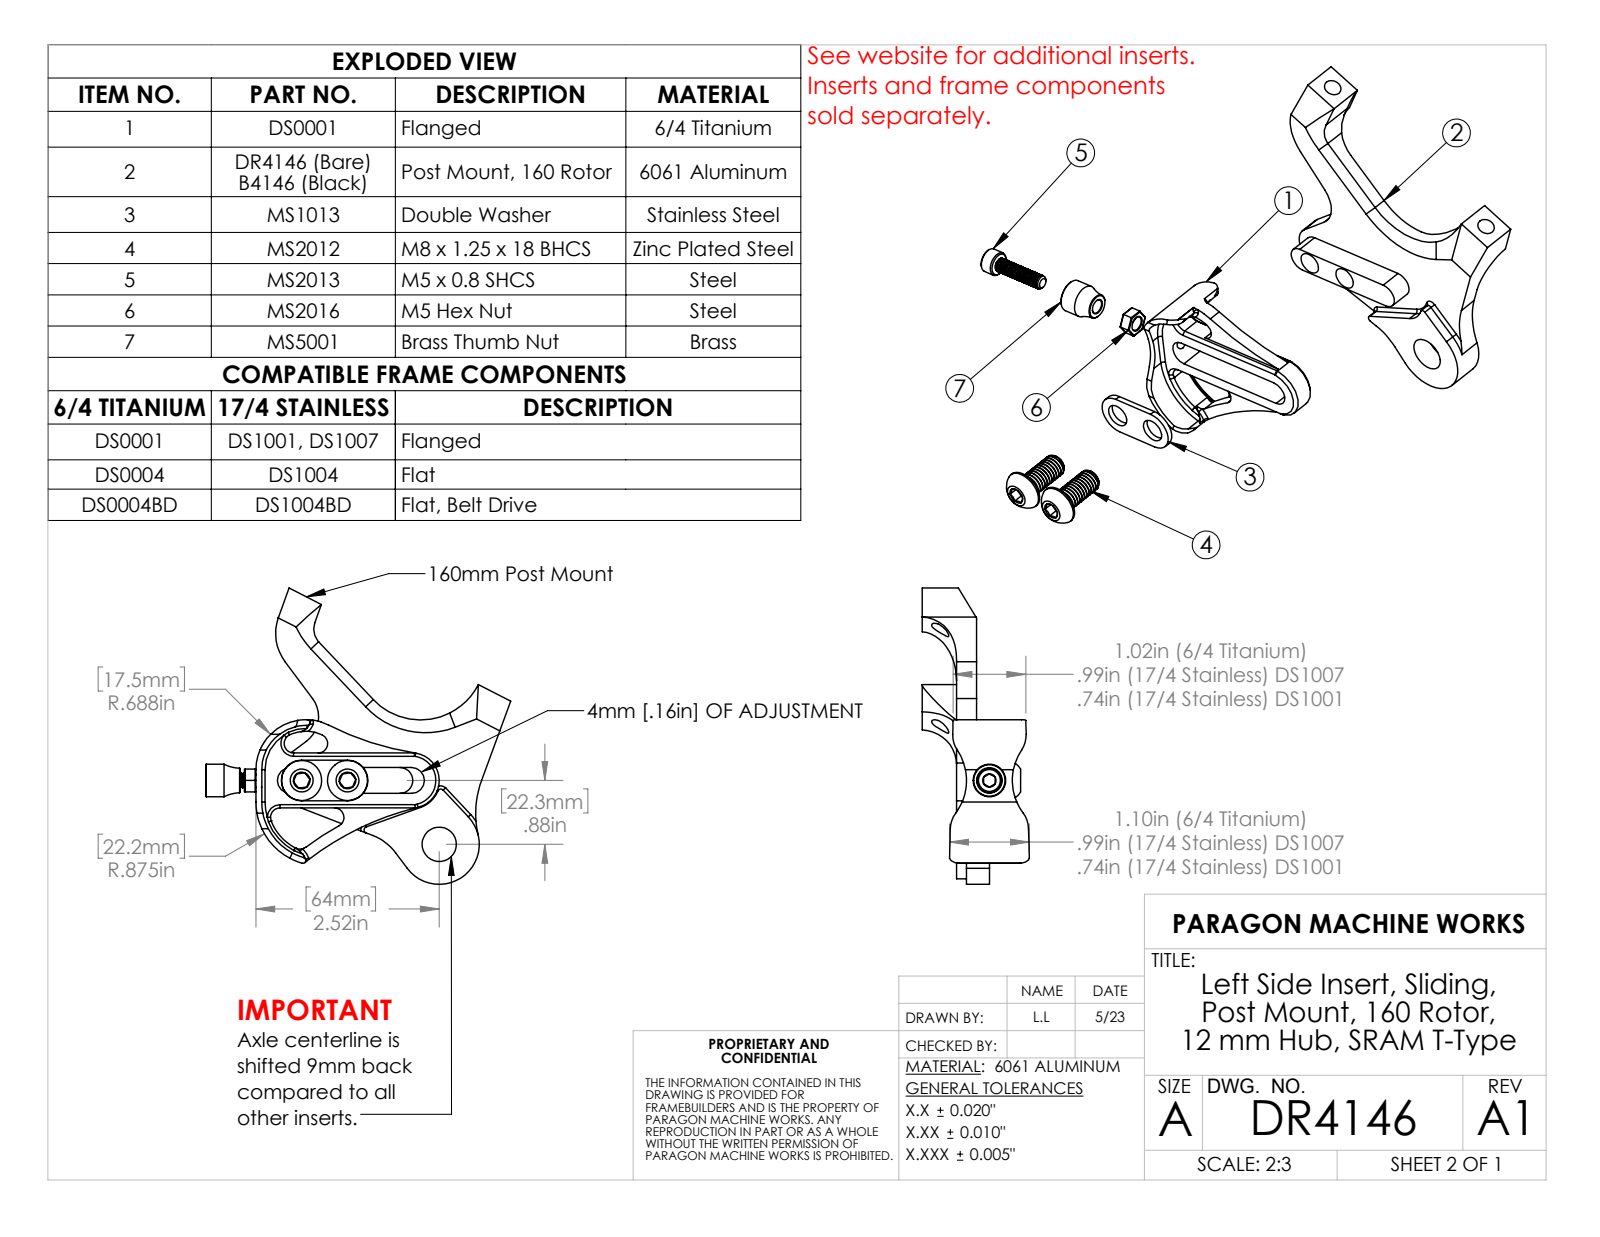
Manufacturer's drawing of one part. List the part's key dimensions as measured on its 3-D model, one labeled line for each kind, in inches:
Part name (STEP PRODUCT): DR4146
STEP written by: SolidWorks 2022 (AUTOMOTIVE_DESIGN)
Units: inches
Bodies: 1 solid, 66 faces (27 planar, 33 cylindrical, 6 other)
Overall size (bounding box): 4.071 × 3.33 × 1.063
Volume: 2.025 in³ · Surface area: 20.81 in²
Round holes (diameter × count): ⌀0.236 ×2, ⌀0.312 ×2, ⌀0.472 ×1
Partial cylindrical surfaces — rounded edges, fillets, slot ends (radius × count): R0.045 ×4, R0.5 ×3, R0.178 ×2, R0.39 ×2, R0.25 ×1, R0.3 ×1, R0.42 ×1, R0.55 ×1
Main face-to-face distances: 0.276, 0.453, 0.177, 0.138, 0.591, 0.315, 0.138, 0.315, 0.356, 0.472
Hole centre spacings: 0.63, 1.537, 2.085, 2.921
